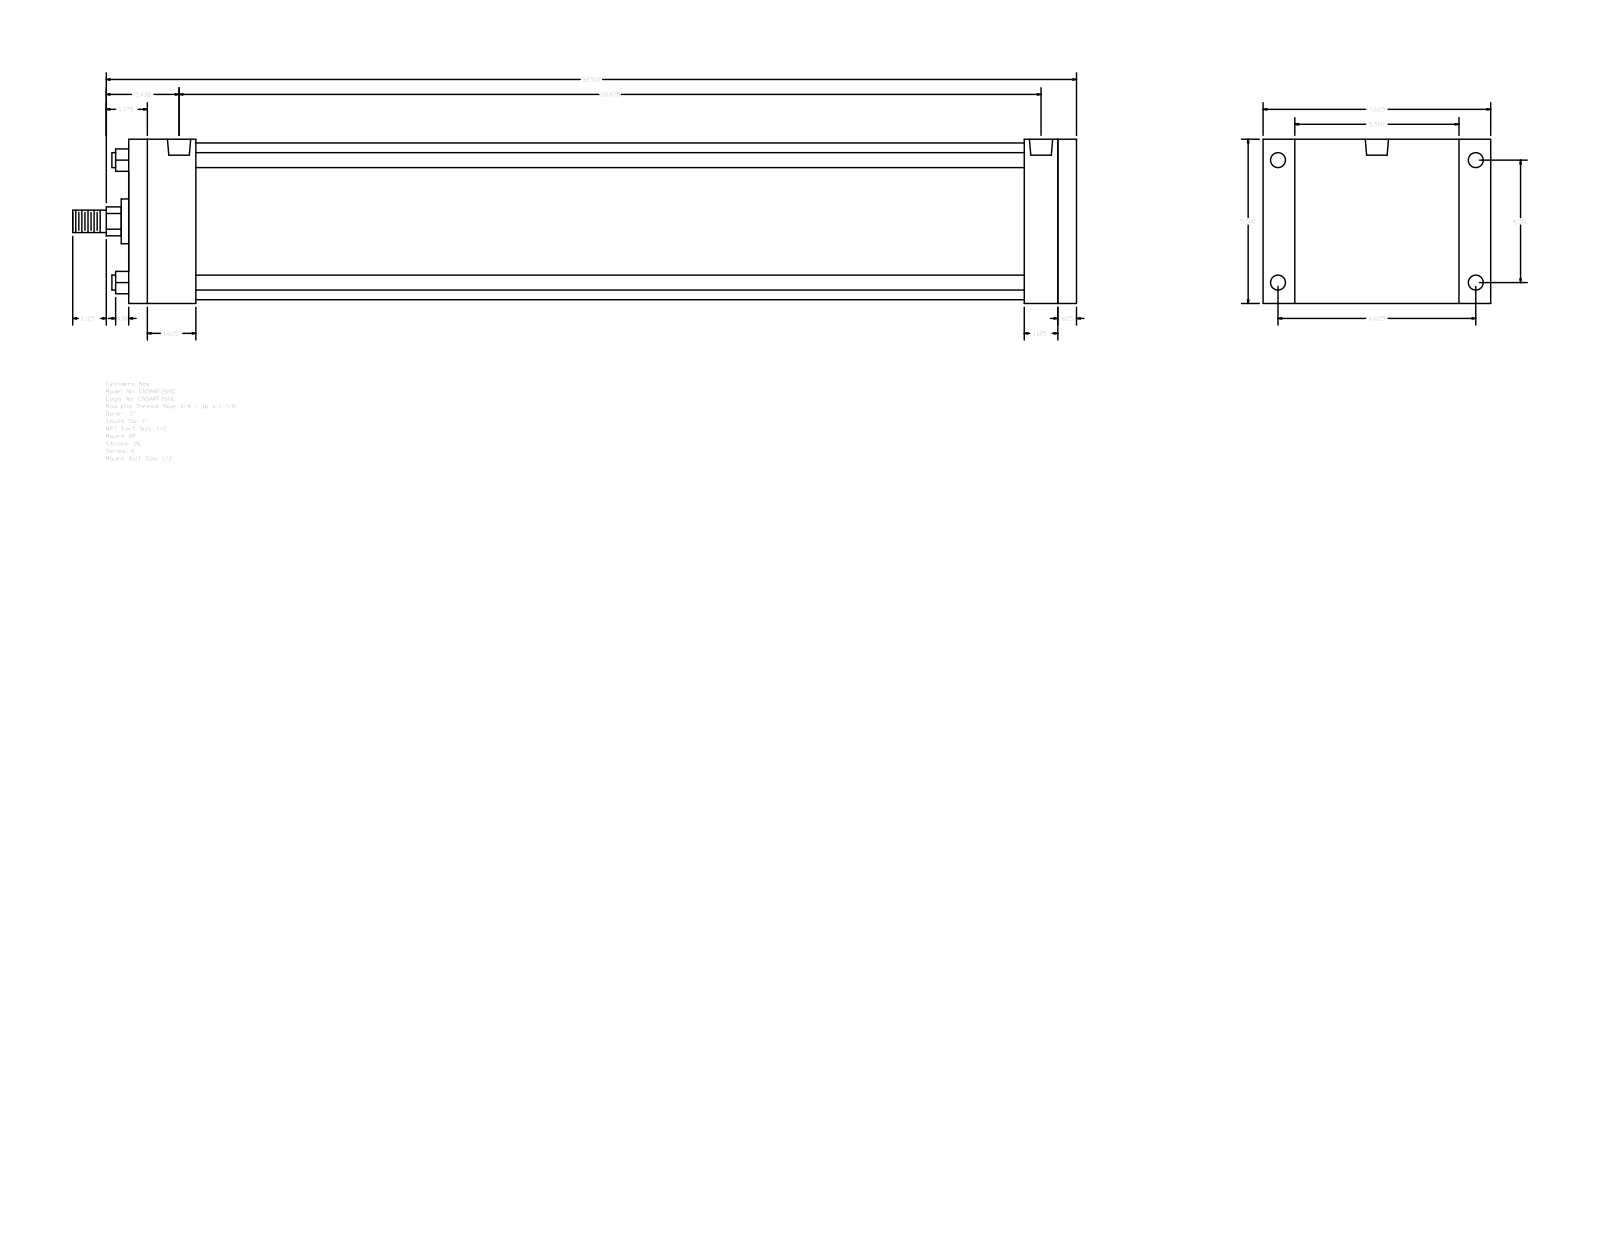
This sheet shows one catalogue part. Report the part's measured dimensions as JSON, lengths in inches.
{"part_name": "A_RF__0500_1", "step_written_by": "GSSL Pune (CONFIG_CONTROL_DESIGN)", "units": "inches", "bodies": {"solids": 0, "faces": 92, "planar": 64, "cylindrical": 28, "other": 0}, "overall_size": [33.625, 7.625, 5.5], "round_holes": [[0.344, 4], [0.5, 4], [0.778, 2]], "round_bosses_or_shafts": [[0.5, 4], [5.25, 1], [1.5, 1], [1, 1], [0.75, 1]], "partial_cylinders_radius": [[0.484, 1]], "face_to_face_distances": [5.5, 31.75, 31.125, 0.625, 1.125, 2.25, 28.875, 29.5, 30, 27.75], "hole_center_spacings": [0.094, 4.1, 6.625, 7.791, 28.687, 28.781, 28.875]}
